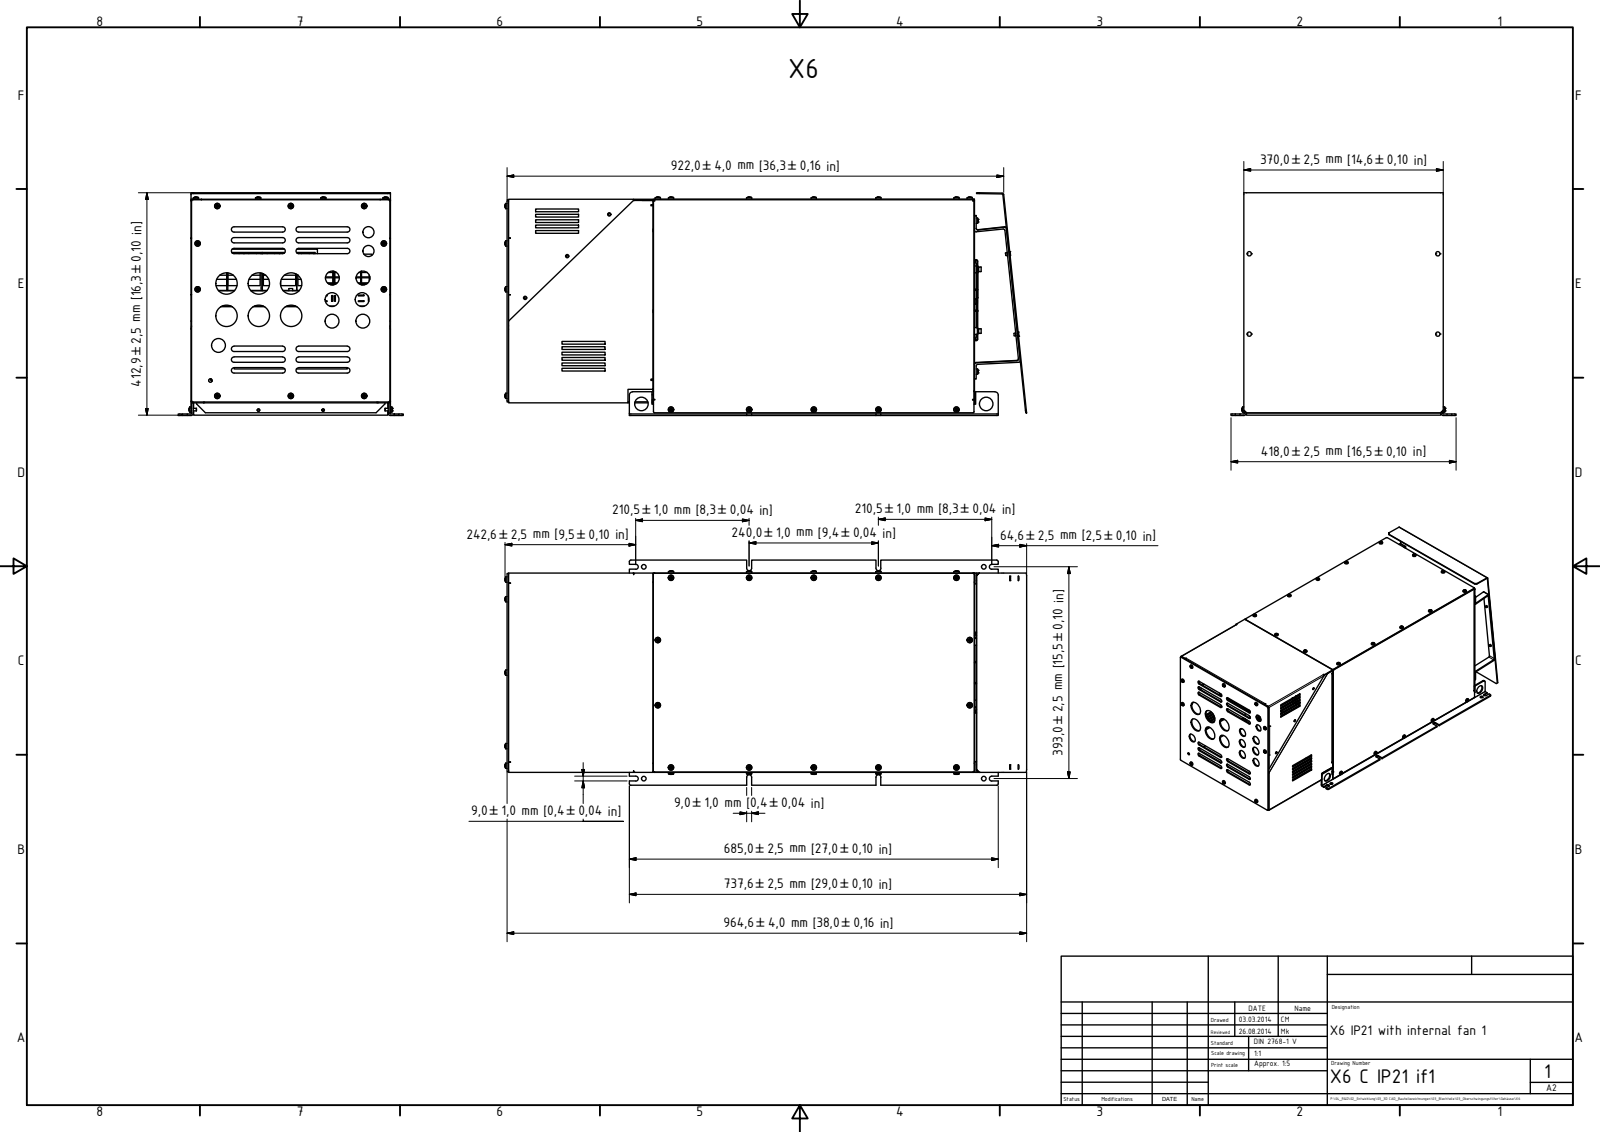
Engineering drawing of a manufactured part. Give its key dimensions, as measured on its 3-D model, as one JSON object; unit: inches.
{"part_name": "10100398 Deckel X5_X6; 10100402 Seitenwand X6; 10100400 Anschlussblech X6; 10100401 Lüfterblech X6 (+8 more)", "step_written_by": "Autodesk Inventor 2015 (AUTOMOTIVE_DESIGN)", "units": "inches", "bodies": {"solids": 143, "faces": 10148, "planar": 6063, "cylindrical": 2408, "other": 1677}, "overall_size": [38.127, 16.457, 16.277], "volume_in3": 285.4, "surface_area_in2": 7629, "round_holes": [[0.163, 40], [0.256, 38], [0.157, 13], [0.325, 12], [0.276, 9], [0.236, 8], [0.354, 8], [0.128, 7], [1.004, 7], [0.335, 6], [1.575, 6], [0.177, 4]], "round_bosses_or_shafts": [[0.197, 41], [0.181, 39], [0.315, 18], [0.709, 12], [0.055, 8], [0.157, 7], [0.335, 5], [0.362, 4]], "partial_cylinders_radius": [[0.009, 112], [0.039, 77], [0.02, 64], [0.006, 54], [0.079, 54], [0.197, 52], [0.118, 43], [0.004, 37]], "face_to_face_distances": [0.039, 0.079, 14.528, 14.488, 0.118, 14.567, 14.843, 14.764, 23.465, 14.882], "hole_center_spacings": [0.827, 4.724, 13.78, 13.858, 1.432, 5.709, 5.906, 10.433]}
